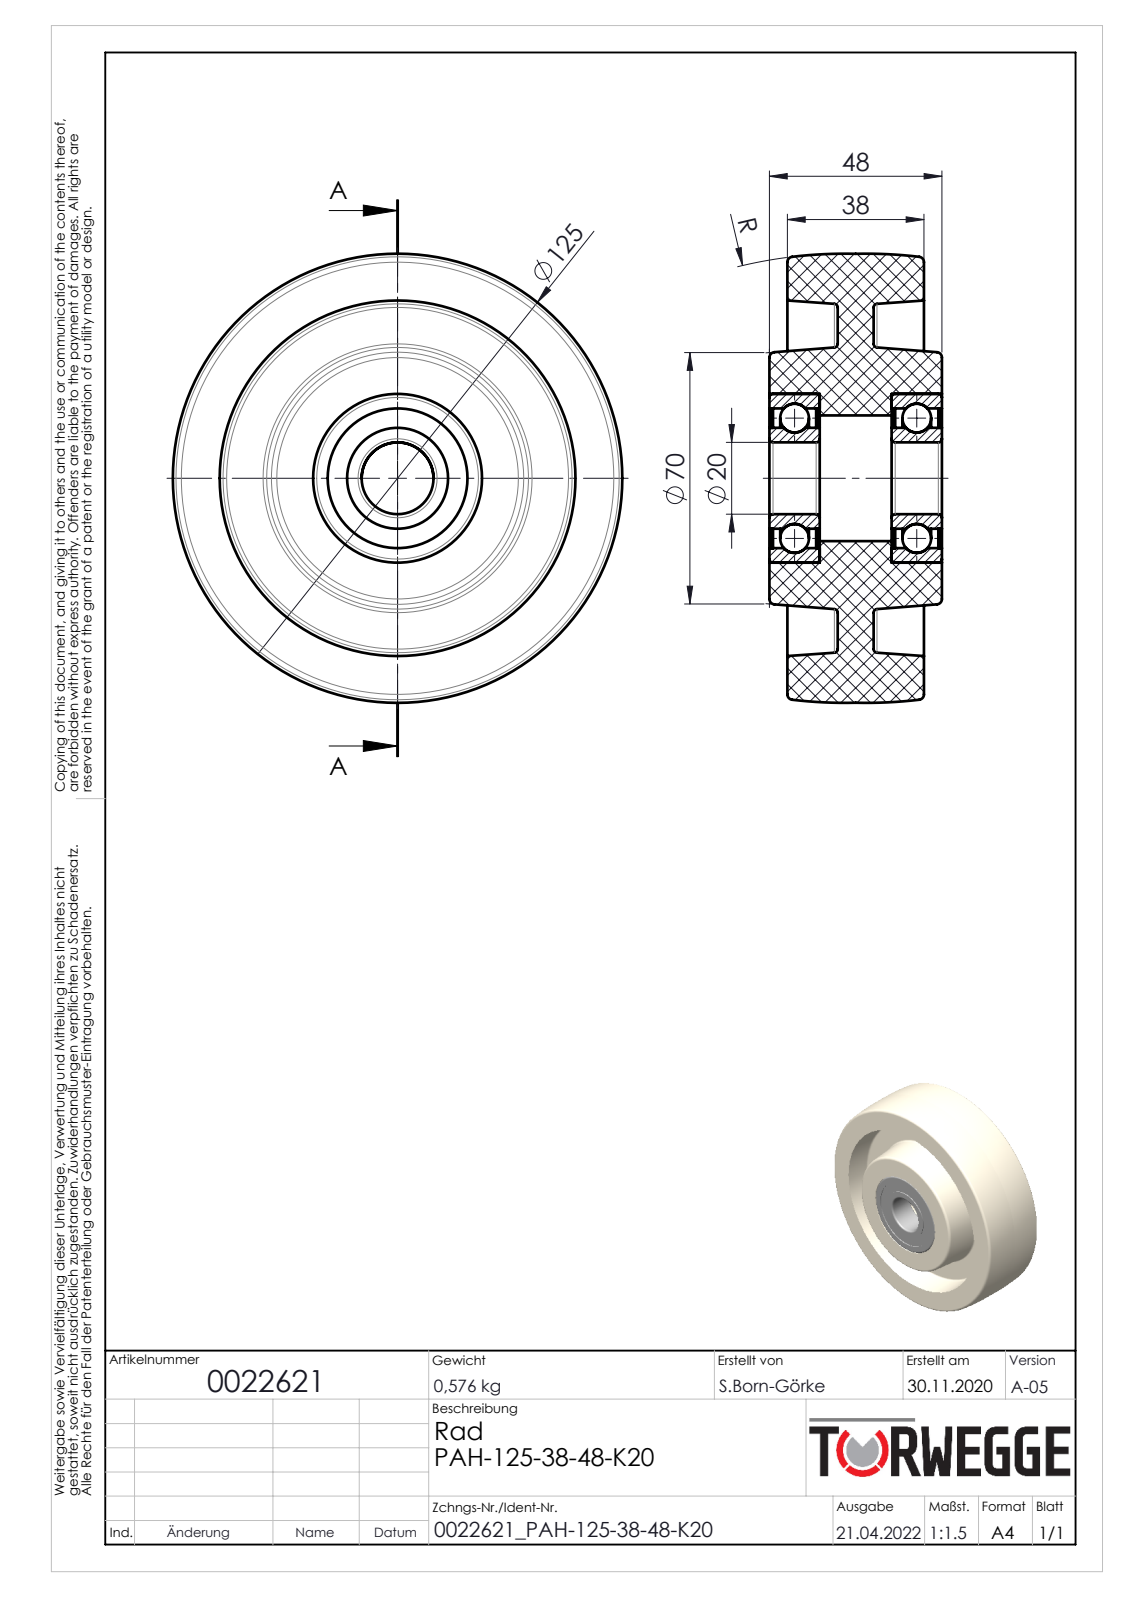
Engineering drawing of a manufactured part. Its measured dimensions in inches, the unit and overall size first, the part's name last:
Units: inches
Overall size (bounding box): 4.924 × 4.924 × 1.89
Round holes (diameter × count): ⌀0.787 ×1, ⌀1.106 ×1, ⌀1.378 ×1, ⌀1.531 ×1, ⌀1.85 ×1
Main face-to-face distances: 0.551, 0.197, 1.142, 0.945, 1.339, 0.748, 1.693, 0.02, 1.496, 0.512
Volume: 22.51 in³ · Surface area: 129.1 in²
Bodies: 11 solids, 138 faces (24 planar, 46 cylindrical, 68 other)
Part name (STEP PRODUCT): 0022621
STEP written by: SolidWorks 2020 (AUTOMOTIVE_DESIGN)
